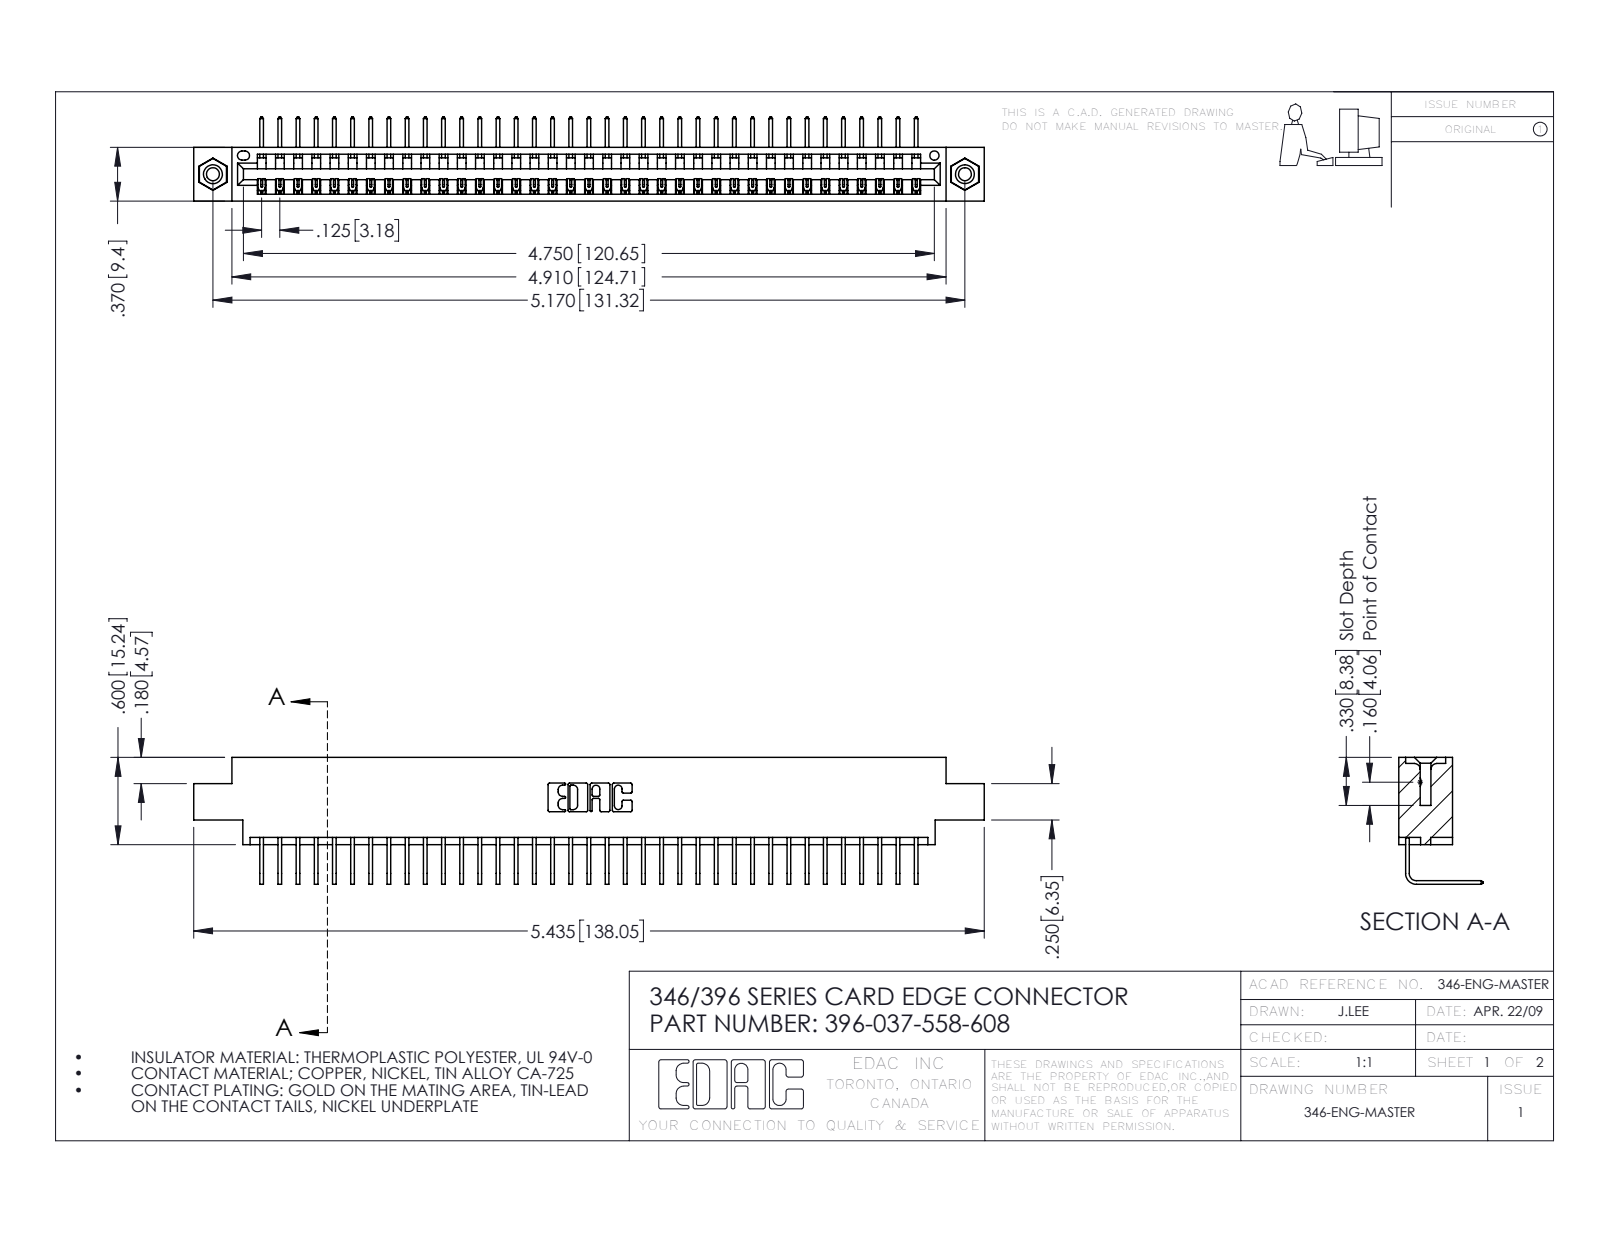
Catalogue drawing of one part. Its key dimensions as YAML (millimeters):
part_name: "346 Part_0.170 Offset - 0.156 Dia-TI; 345-250-001_345-250-003-102; 345-292-001_558 Tail - 2; 396-037-558-608"
step_written_by: "SolidWorks 2016 (CONFIG_CONTROL_DESIGN)"
units: millimeters
bodies: {solids: 40, faces: 2406, planar: 1666, cylindrical: 724, other: 16}
overall_size: [138, 22.2, 14.7]
volume: 13100
surface_area: 17290
round_holes:
  - {diameter: 2.3, count: 2}
  - {diameter: 3.2, count: 2}
  - {diameter: 4, count: 2}
  - {diameter: 1.6, count: 1}
round_bosses_or_shafts:
  - {diameter: 3.9, count: 2}
partial_cylinders:
  - {radius: 0.2, count: 74}
  - {radius: 0.3, count: 22}
  - {radius: 0.2, count: 6}
  - {radius: 0.8, count: 6}
  - {radius: 0.7, count: 3}
  - {radius: 0.8, count: 2}
  - {radius: 1, count: 2}
  - {radius: 0.4, count: 1}
face_to_face_distances: [8.2, 1.2, 9.4, 6.4, 7.6, 0.6, 1.8, 5.6, 3.8, 2.5]
hole_center_spacings: [6.2, 126, 131.3]
